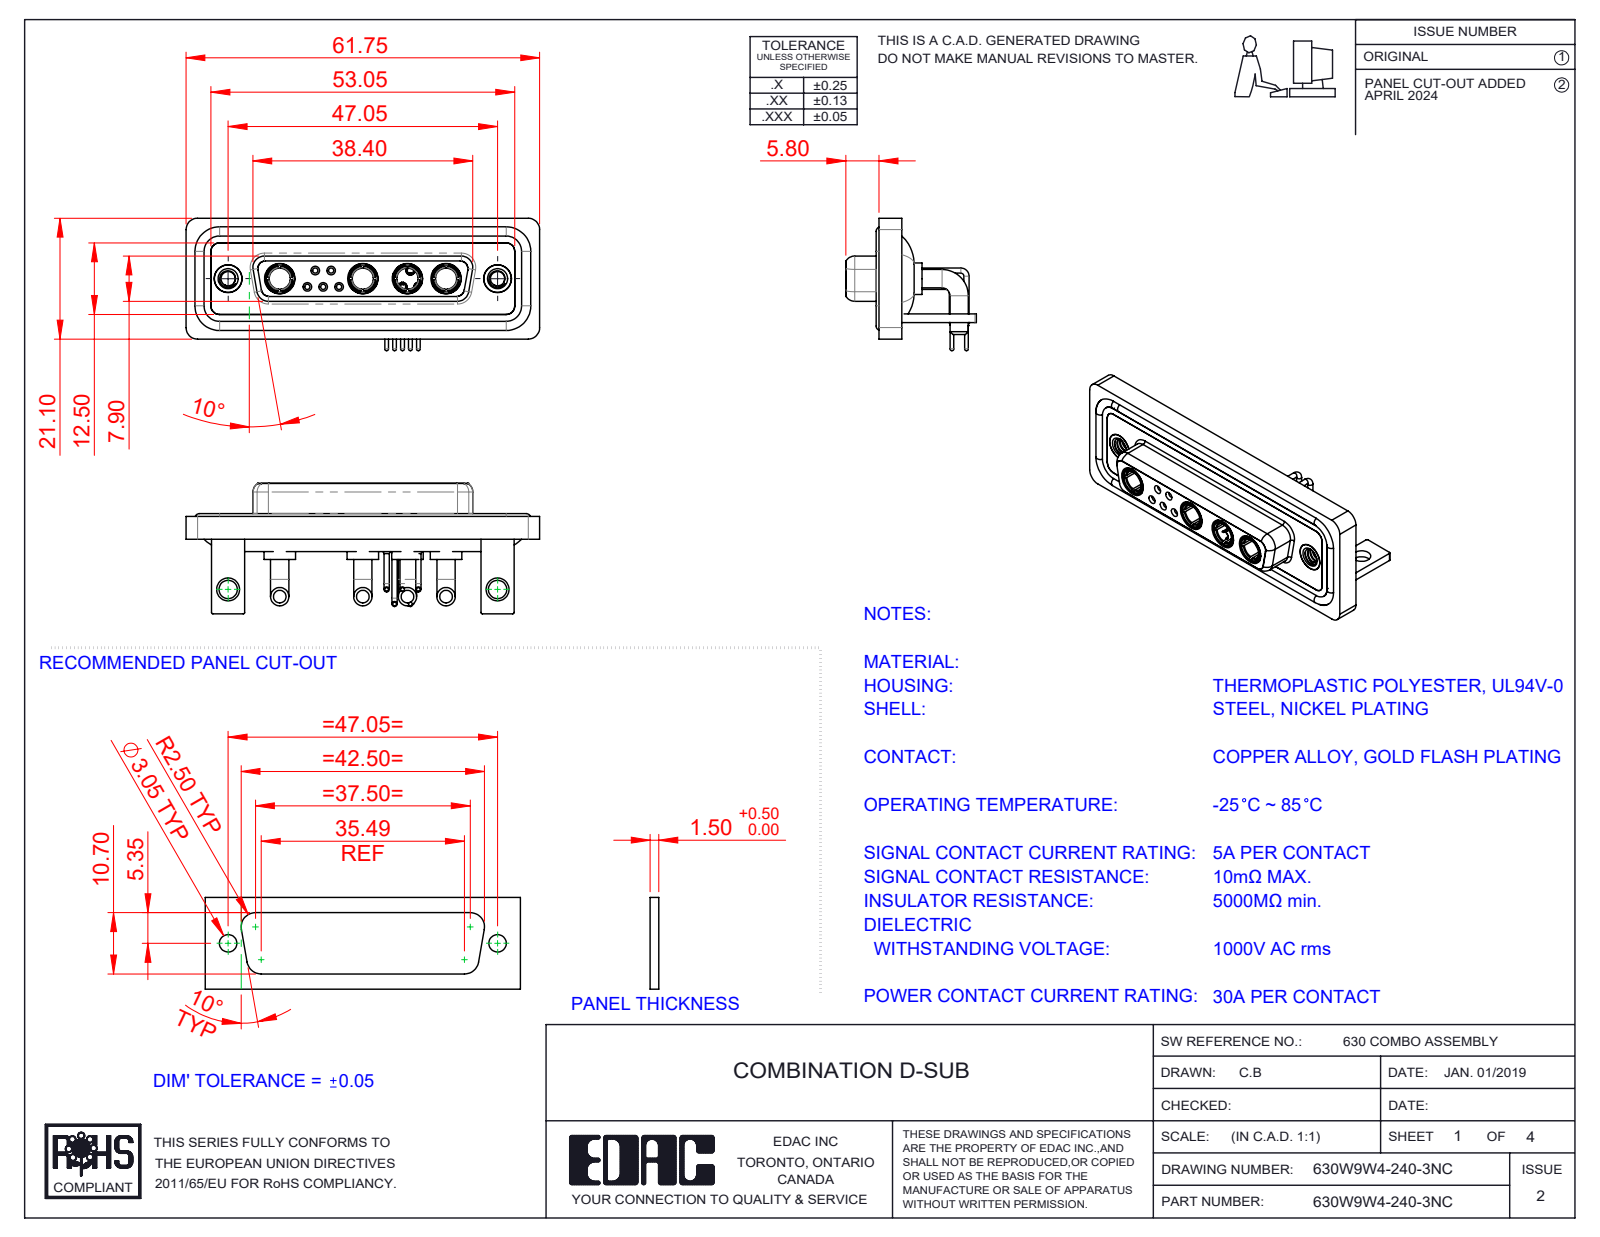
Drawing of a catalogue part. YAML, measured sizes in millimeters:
part_name: "630Combo Waterproof Housing_25 Contacts; 630Combo Shell Rear_25 Contacts; 630Combo Shell Front_25 Contacts; 630Combo Stabilizer Bracket_50 Contacts (+6 more)"
step_written_by: "SolidWorks 2023 (CONFIG_CONTROL_DESIGN)"
units: millimeters
bodies: {solids: 22, faces: 1005, planar: 316, cylindrical: 425, other: 264}
overall_size: [61.75, 23.12, 22.8]
volume: 8923
surface_area: 14859
round_holes:
  - {diameter: 4.85, count: 6}
  - {diameter: 0.9, count: 5}
  - {diameter: 1.1, count: 5}
  - {diameter: 1.5, count: 5}
  - {diameter: 2, count: 5}
  - {diameter: 3.7, count: 4}
  - {diameter: 5.3, count: 4}
  - {diameter: 1.6, count: 3}
  - {diameter: 1.7, count: 2}
  - {diameter: 2.5, count: 2}
  - {diameter: 3.2, count: 2}
  - {diameter: 4, count: 2}
round_bosses_or_shafts:
  - {diameter: 0.9, count: 10}
  - {diameter: 1.6, count: 9}
  - {diameter: 3.2, count: 8}
  - {diameter: 2, count: 5}
  - {diameter: 1.5, count: 5}
  - {diameter: 0.65, count: 5}
  - {diameter: 5.5, count: 4}
  - {diameter: 5.2, count: 4}
partial_cylinders:
  - {radius: 2, count: 19}
  - {radius: 1.5, count: 18}
  - {radius: 0.25, count: 16}
  - {radius: 1.35, count: 8}
  - {radius: 1.6, count: 8}
  - {radius: 0.5, count: 5}
  - {radius: 0.6, count: 4}
  - {radius: 0.65, count: 4}
face_to_face_distances: [0.4, 1.8, 2.9, 3.7, 1.5, 4.1, 1.1, 1.4, 1.6, 2.5]
hole_center_spacings: [3.16, 2.77, 5.04, 13.85, 11.08, 12.79, 15.5, 5.54]
